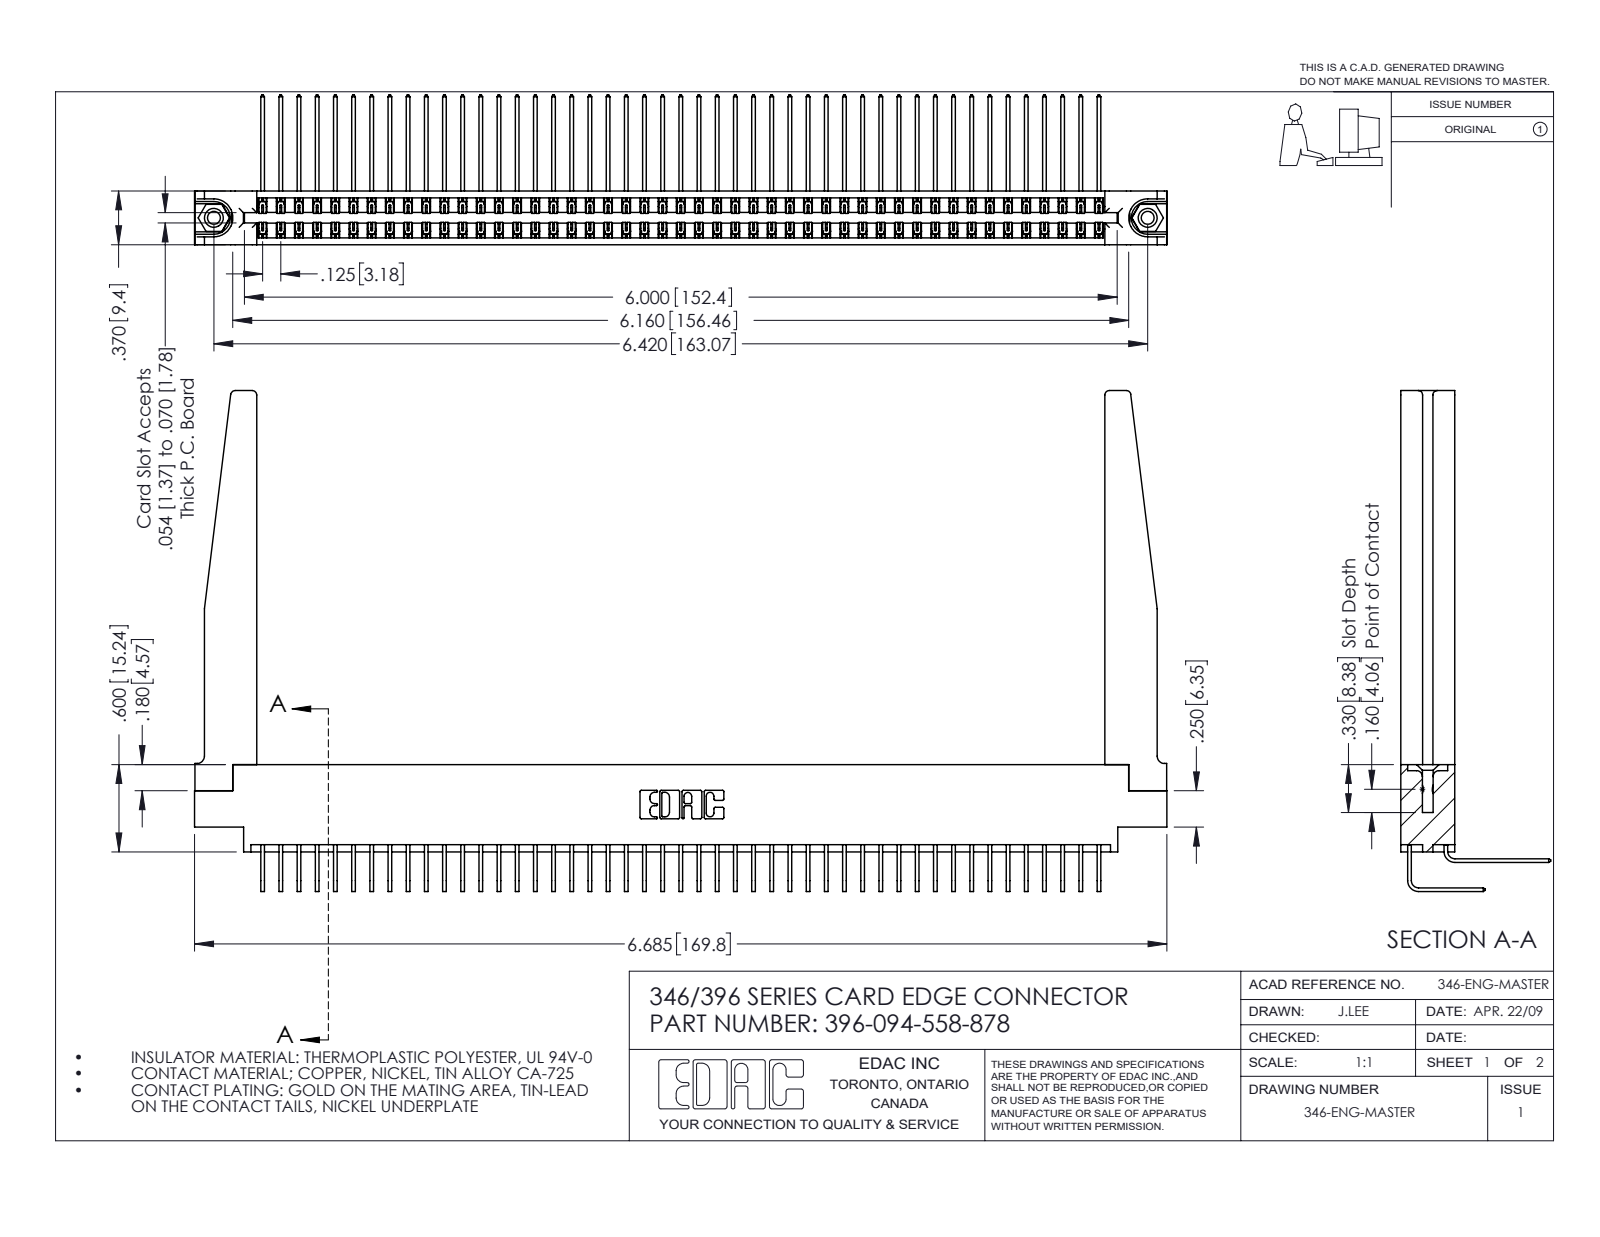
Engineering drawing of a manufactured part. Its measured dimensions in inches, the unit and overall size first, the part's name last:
Units: inches
Overall size (bounding box): 6.685 × 3.443 × 1.03
Round holes (diameter × count): ⌀0.089 ×2, ⌀0.125 ×2, ⌀0.156 ×2, ⌀0.064 ×1
Round bosses / shafts (diameter × count): ⌀0.155 ×2
Partial cylindrical surfaces — rounded edges, fillets, slot ends (radius × count): R0.006 ×141, R0.01 ×22, R0.03 ×8, R0.007 ×6, R0.031 ×6, R0.05 ×4, R0.026 ×3, R0.014 ×2
Main face-to-face distances: 0.322, 0.37, 0.048, 0.072, 0.025, 0.298, 0.25, 0.148, 0.15, 0.275
Hole centre spacings: 0.246, 6.211, 6.42
Volume: 1.458 in³ · Surface area: 50.75 in²
Bodies: 99 solids, 5436 faces (3700 planar, 1684 cylindrical, 52 other)
Part name (STEP PRODUCT): 345-250-001_345-250-001-102; 345-292-001_558 559 Tail - 1; 345-292-001_558 Tail - 2; 346-220-078_345-220-078 (+2 more)
STEP written by: SolidWorks 2016 (CONFIG_CONTROL_DESIGN)
